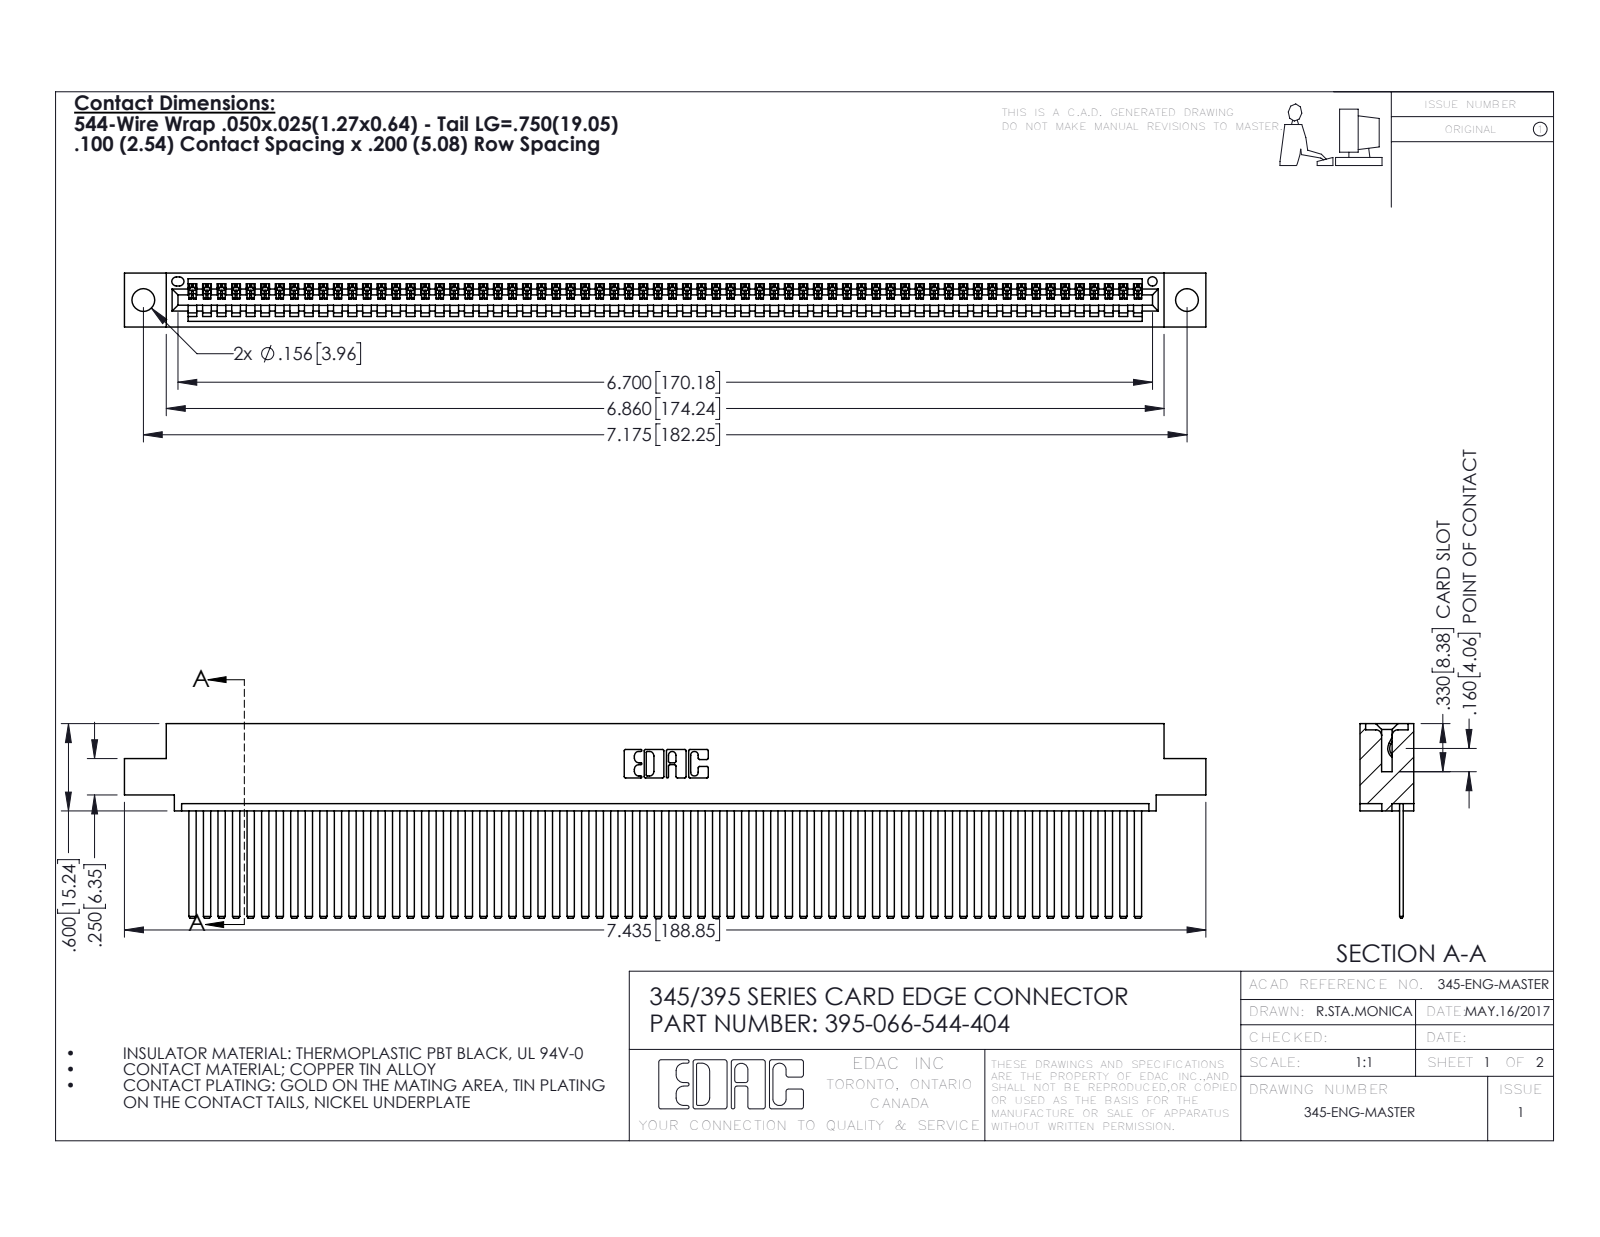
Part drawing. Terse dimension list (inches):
name: 395-066-544-404; 345 Part_0.110 Offset - 0.156 Dia-TH; 345-292-001_345-293-144
written by: SolidWorks 2016 (CONFIG_CONTROL_DESIGN)
unit: in
bodies: 67 solids, 3562 faces (2460 planar, 1102 cylindrical, 0 other)
size: 7.435 × 1.337 × 0.37
volume: 1.143 in³; area: 42.49 in²
holes: 2× ⌀0.156, 1× ⌀0.064
rounds: 132× R0.006, 22× R0.01, 6× R0.007, 6× R0.031, 3× R0.026, 2× R0.031, 2× R0.04, 1× R0.014
face distances: 0.072, 0.298, 0.025, 0.098, 0.272, 0.37, 0.2, 0.225, 0.149, 0.072
hole spacings: 0.27, 6.939, 7.175
